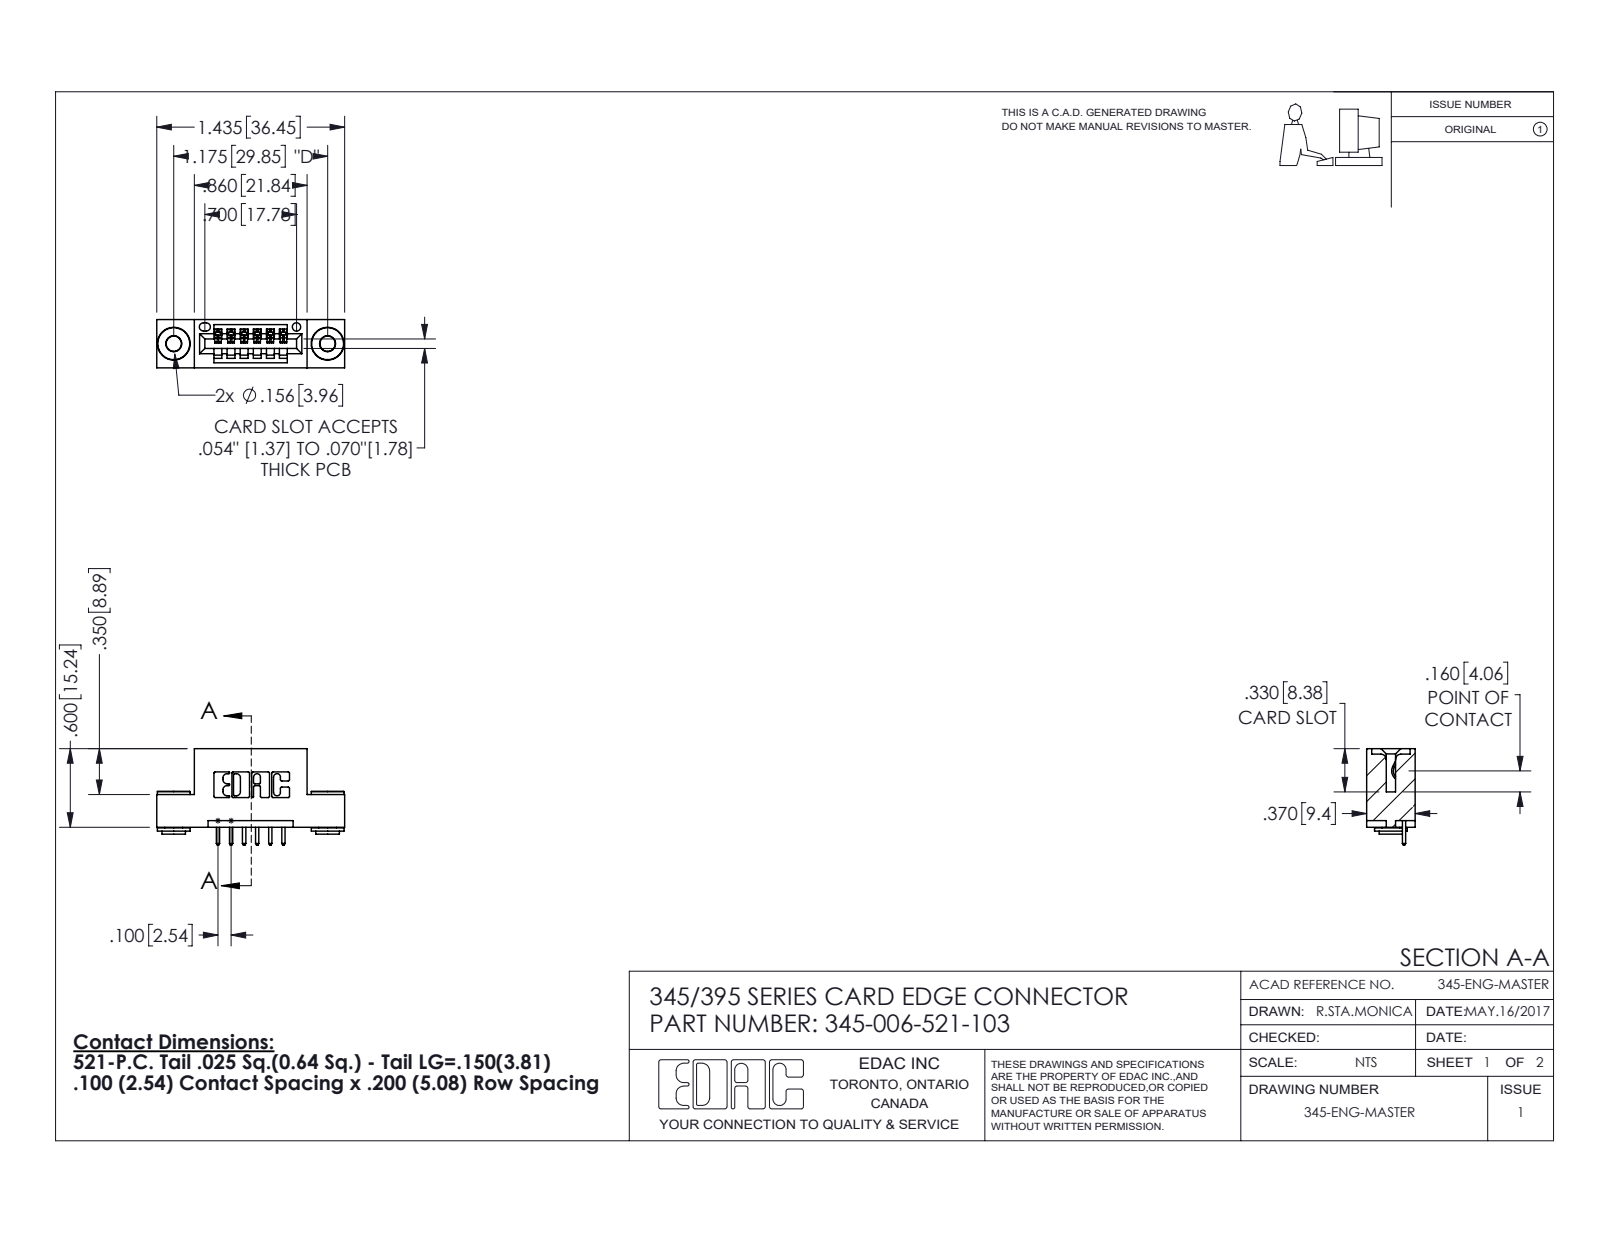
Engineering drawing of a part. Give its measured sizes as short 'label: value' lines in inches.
name: 345-006-521-103; 345-250-002_345-250-002-102; 345-292-001_345-293-121; 345 Part_Flush Mounting Lugs - 0.156 Dia-TH
written by: SolidWorks 2016 (CONFIG_CONTROL_DESIGN)
unit: in
bodies: 9 solids, 512 faces (330 planar, 174 cylindrical, 8 other)
size: 1.435 × 0.737 × 0.37
volume: 0.193 in³; area: 5.999 in²
holes: 2× ⌀0.116, 2× ⌀0.156, 1× ⌀0.064
bosses: 2× ⌀0.25, 2× ⌀0.18, 2× ⌀0.136
rounds: 22× R0.01, 12× R0.006, 12× R0.01, 6× R0.007, 6× R0.031, 3× R0.026, 2× R0.031, 2× R0.04
face distances: 0.2, 0.37, 0.072, 0.298, 0.1, 0.025, 0.25, 0.3, 0.098, 0.272
hole spacings: 0.27, 0.946, 1.175
